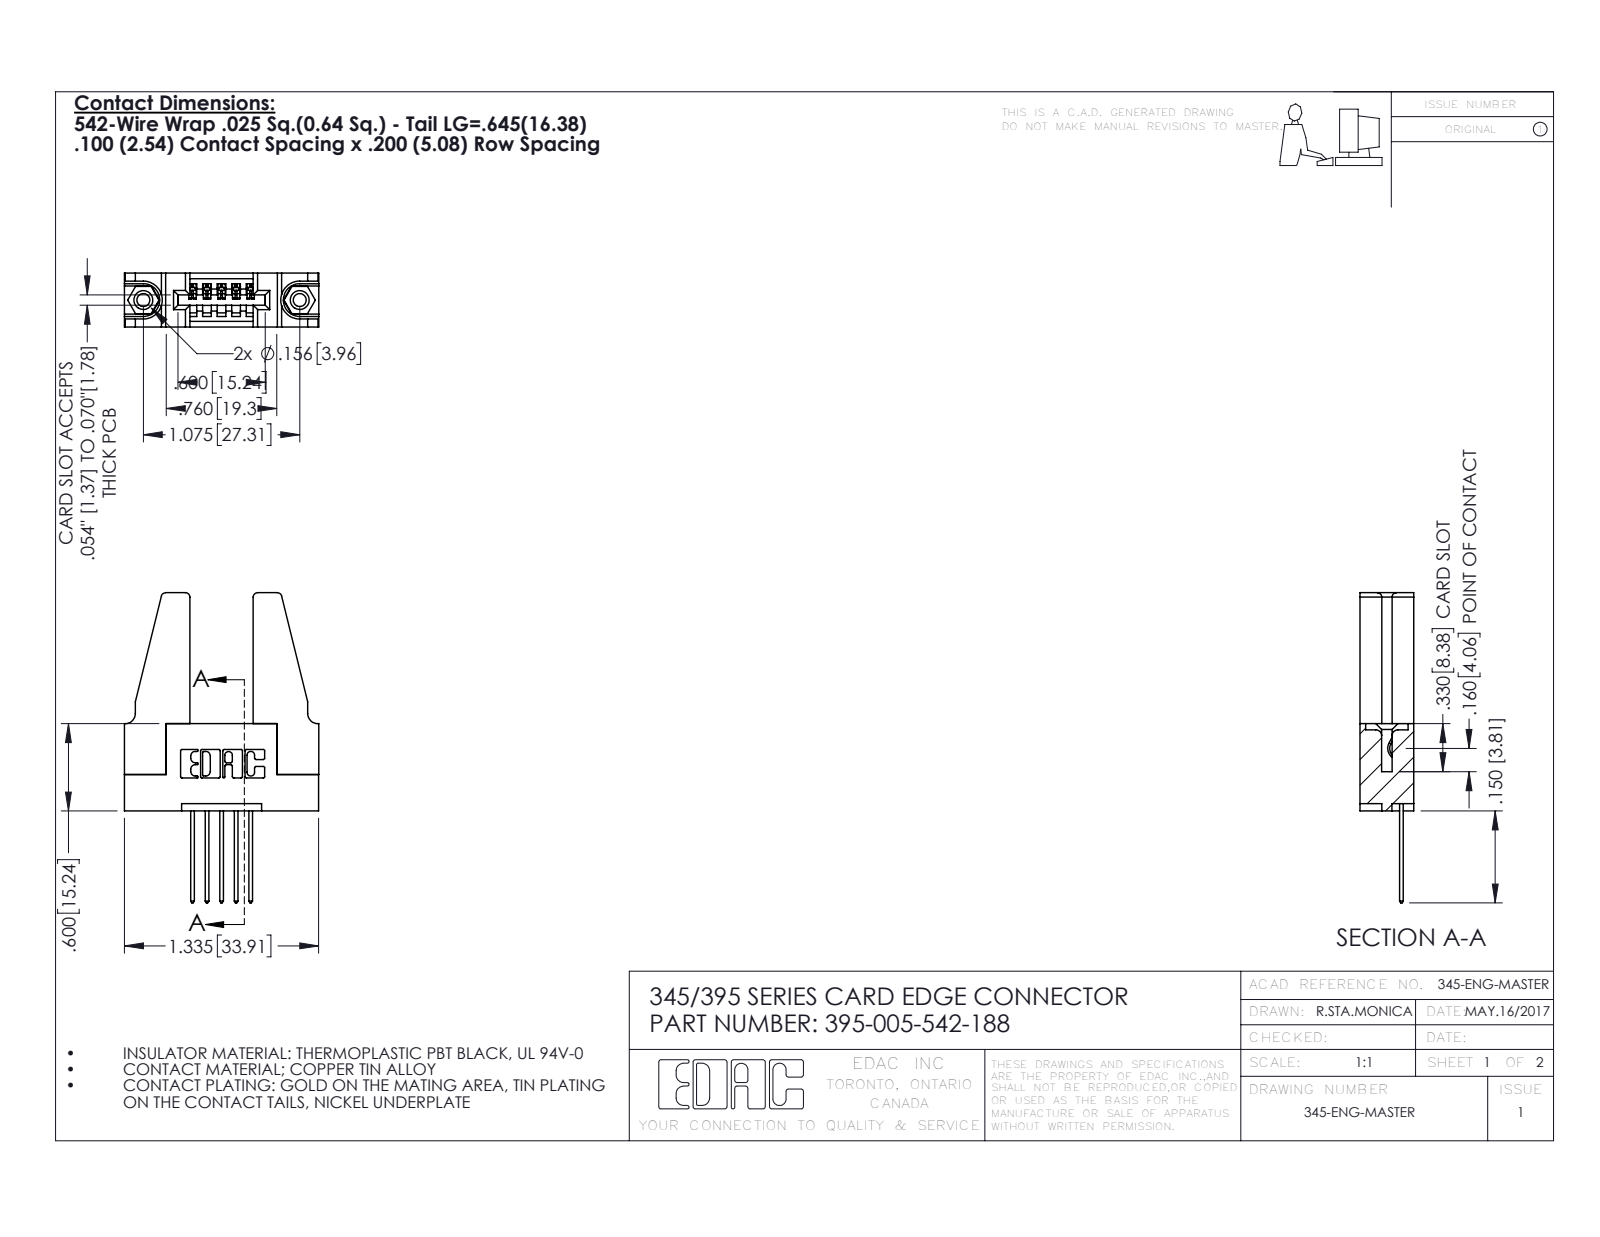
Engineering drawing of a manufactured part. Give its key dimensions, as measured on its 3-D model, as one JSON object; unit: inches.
{"part_name": "345-220-078_345-220-088; 395-005-542-188; 345-292-001_345-293-142; 345-250-001_345-250-001-102 (+1 more)", "step_written_by": "SolidWorks 2016 (CONFIG_CONTROL_DESIGN)", "units": "inches", "bodies": {"solids": 10, "faces": 540, "planar": 352, "cylindrical": 172, "other": 16}, "overall_size": [2.132, 1.336, 0.37], "volume_in3": 0.377, "surface_area_in2": 10.22, "round_holes": [[0.089, 2], [0.125, 2], [0.156, 2], [0.064, 1]], "round_bosses_or_shafts": [[0.155, 2]], "partial_cylinders_radius": [[0.01, 22], [0.006, 10], [0.01, 10], [0.03, 8], [0.007, 6], [0.031, 6], [0.026, 3], [0.031, 2]], "face_to_face_distances": [0.37, 0.2, 0.072, 0.298, 0.598, 0.25, 0.148, 0.15, 0.35, 0.098], "hole_center_spacings": [0.27, 0.847, 1.075]}
